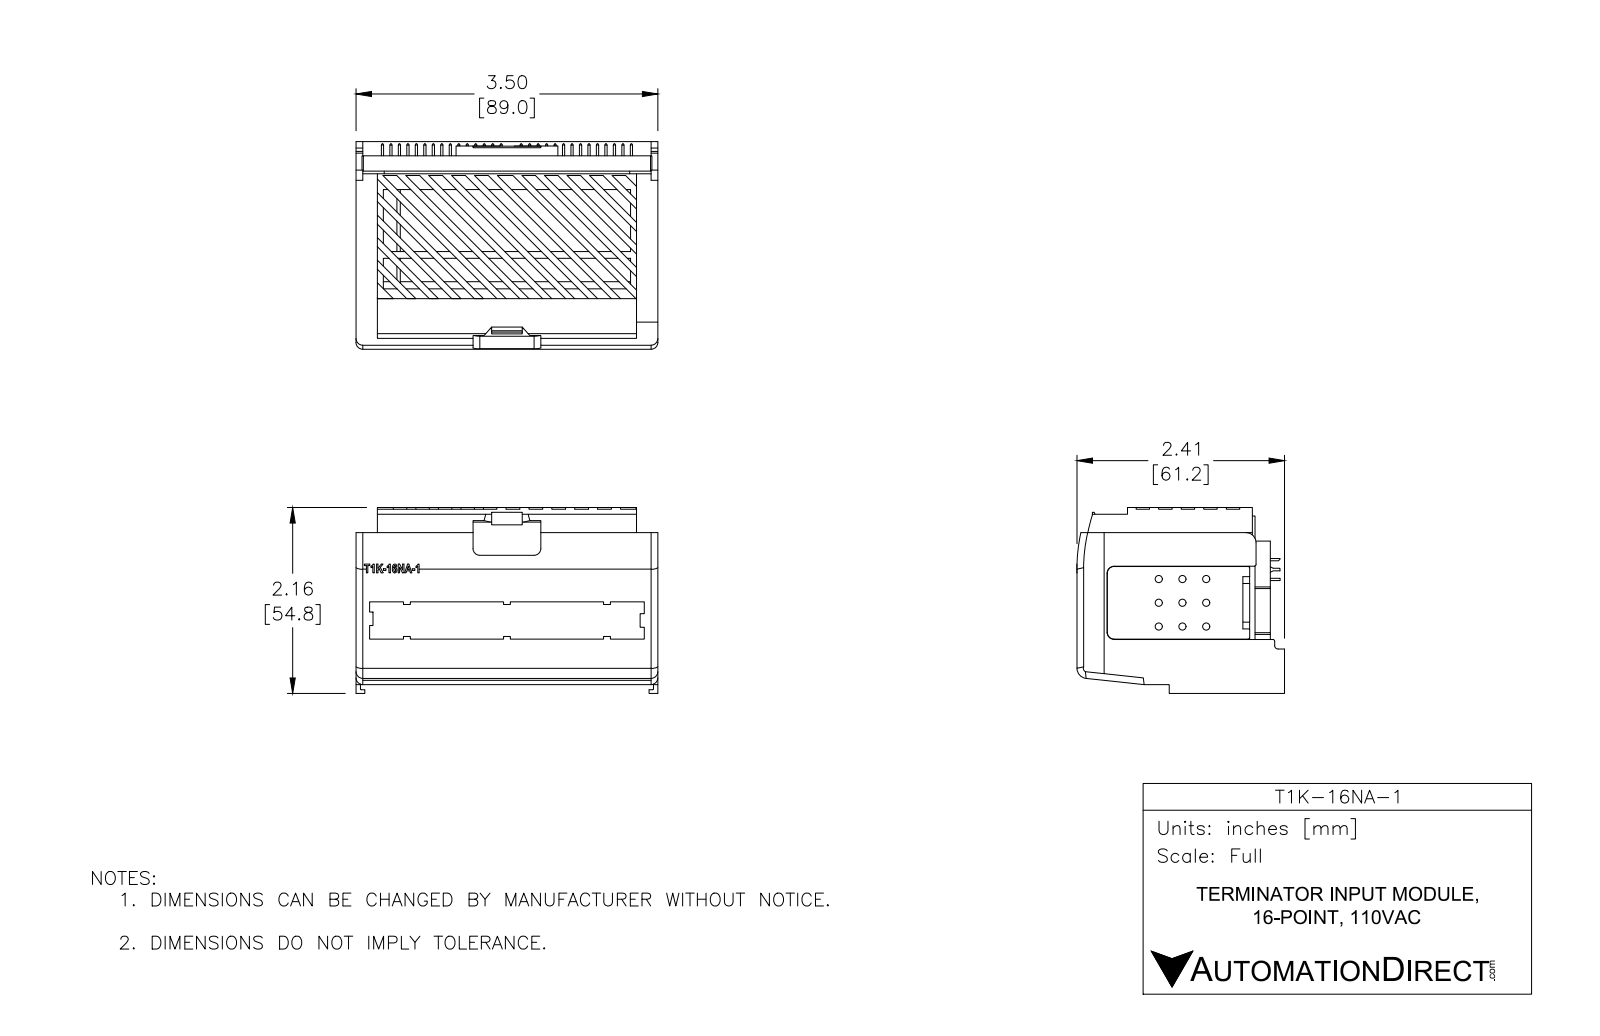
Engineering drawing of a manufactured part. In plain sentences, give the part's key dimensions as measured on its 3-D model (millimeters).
The part is named "T1K-16NA-1". Its 3-D file was written by "SolidWorks 2013 (AUTOMOTIVE_DESIGN)". It is 1 solid with 644 faces: 453 planar, 181 cylindrical and 10 other. Overall it measures 88.7 by 65.1 by 61.36 millimeters. Its volume is 45 450 cubic millimeters and its surface area 54 523 square millimeters. Round holes: 16 of diameter 3. Round bosses or shafts: 56 of diameter 0.7. Partial cylindrical surfaces (rounded edges, fillets, slot ends): 18 of radius 3.5, 5 of radius 1, 3 of radius 0.25, 3 of radius 0.55, 2 of radius 1.5, 1 of radius 8, 1 of radius 10, 1 of radius 18. The main face-to-face distances are 2, 86.7, 55.35, 0.5, 59.8, 88.7, 1.5, 55.26, 53.35, 84.7. The hole center spacings are 5.15, 10.3, 15.45, 20.6, 25.75, 30.9, 36.05, 41.2.
